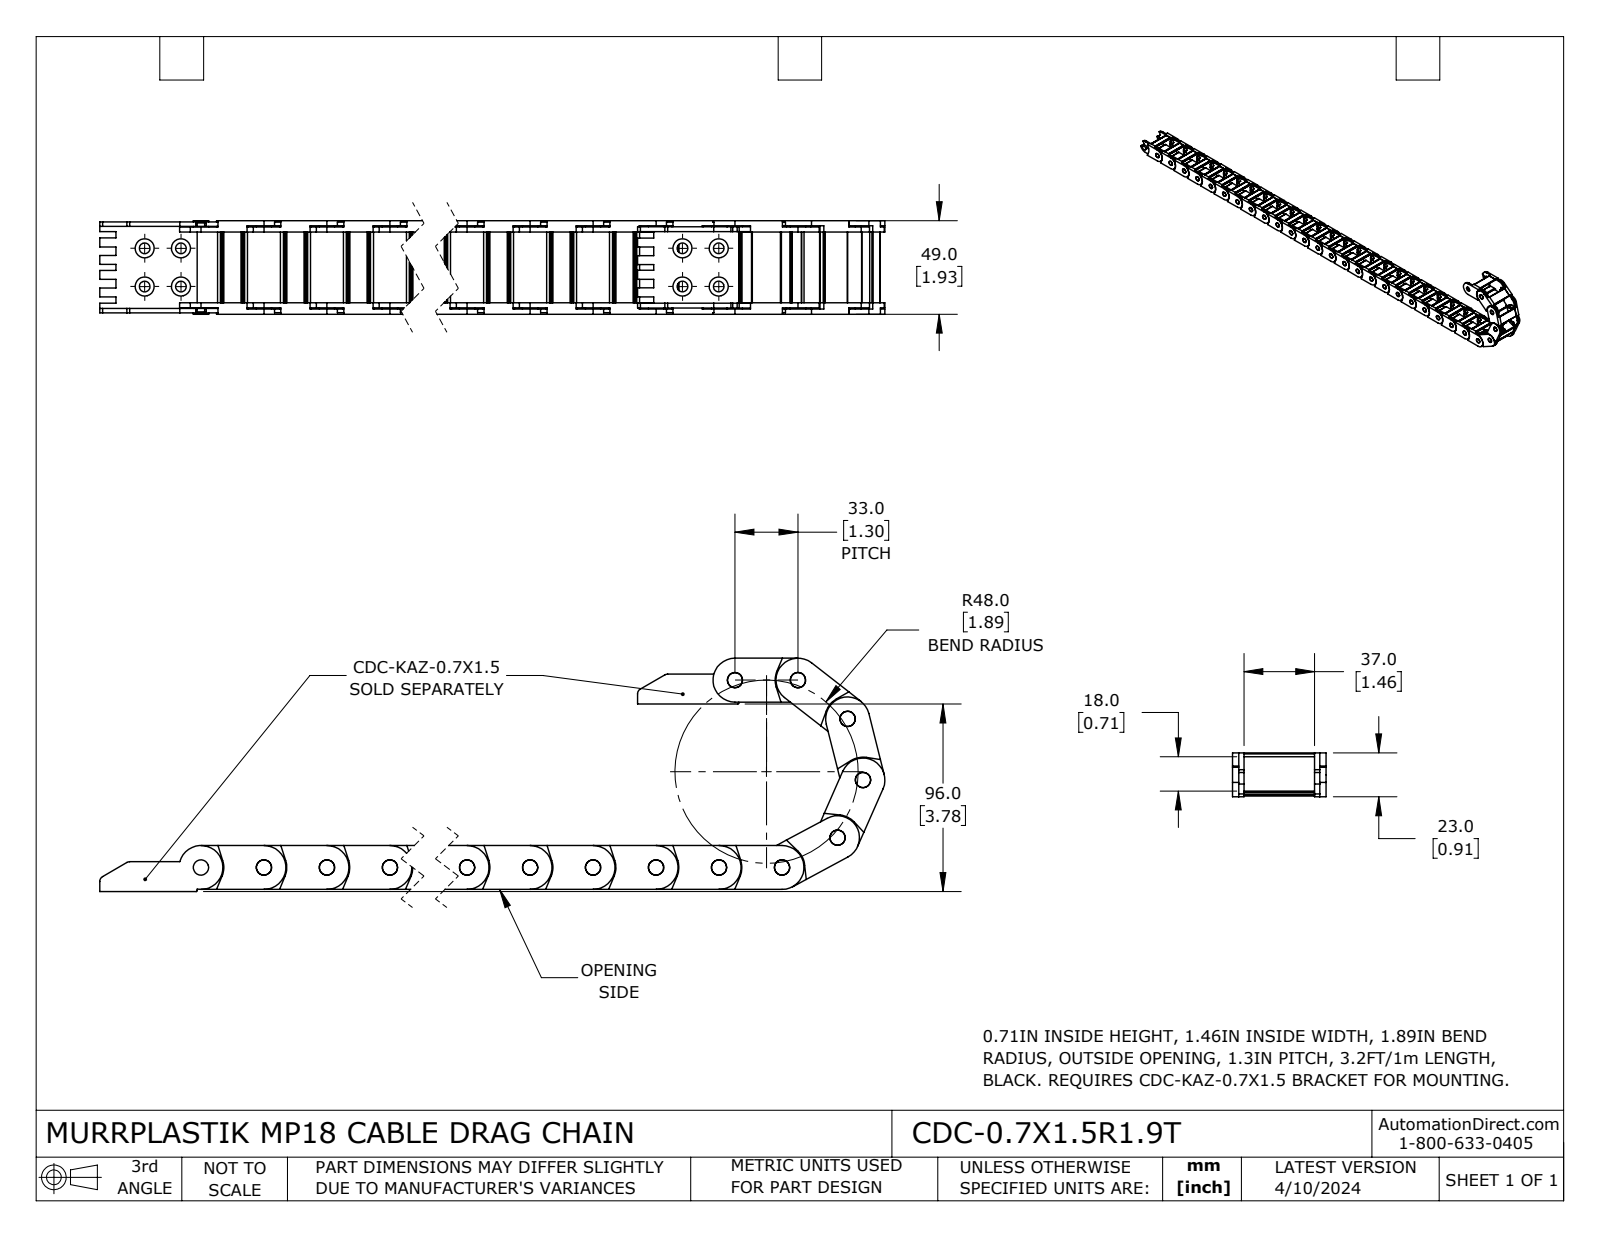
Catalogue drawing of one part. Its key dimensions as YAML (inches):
part_name: "CDC-0.7X1.5R1.9T"
step_written_by: "SolidWorks 2023 (CONFIG_CONTROL_DESIGN)"
units: inches
bodies: {solids: 30, faces: 2280, planar: 1110, cylindrical: 1170, other: 0}
overall_size: [35.043, 4.767, 1.929]
volume: 17.66
surface_area: 370.1
round_holes:
  - {diameter: 0.315, count: 30}
round_bosses_or_shafts:
  - {diameter: 0.315, count: 1}
partial_cylinders:
  - {radius: 0.02, count: 120}
  - {radius: 0.059, count: 120}
  - {radius: 0.008, count: 60}
  - {radius: 0.012, count: 60}
  - {radius: 0.453, count: 31}
  - {radius: 0.47, count: 31}
  - {radius: 0.197, count: 30}
  - {radius: 0.215, count: 30}
face_to_face_distances: [1.693, 0.106, 0.13, 0.236, 1.929, 1.799, 1.563, 1.823, 0.024, 1.587]
hole_center_spacings: [1.299, 2.598, 3.898, 5.197, 6.496, 7.795, 9.094, 10.394]
